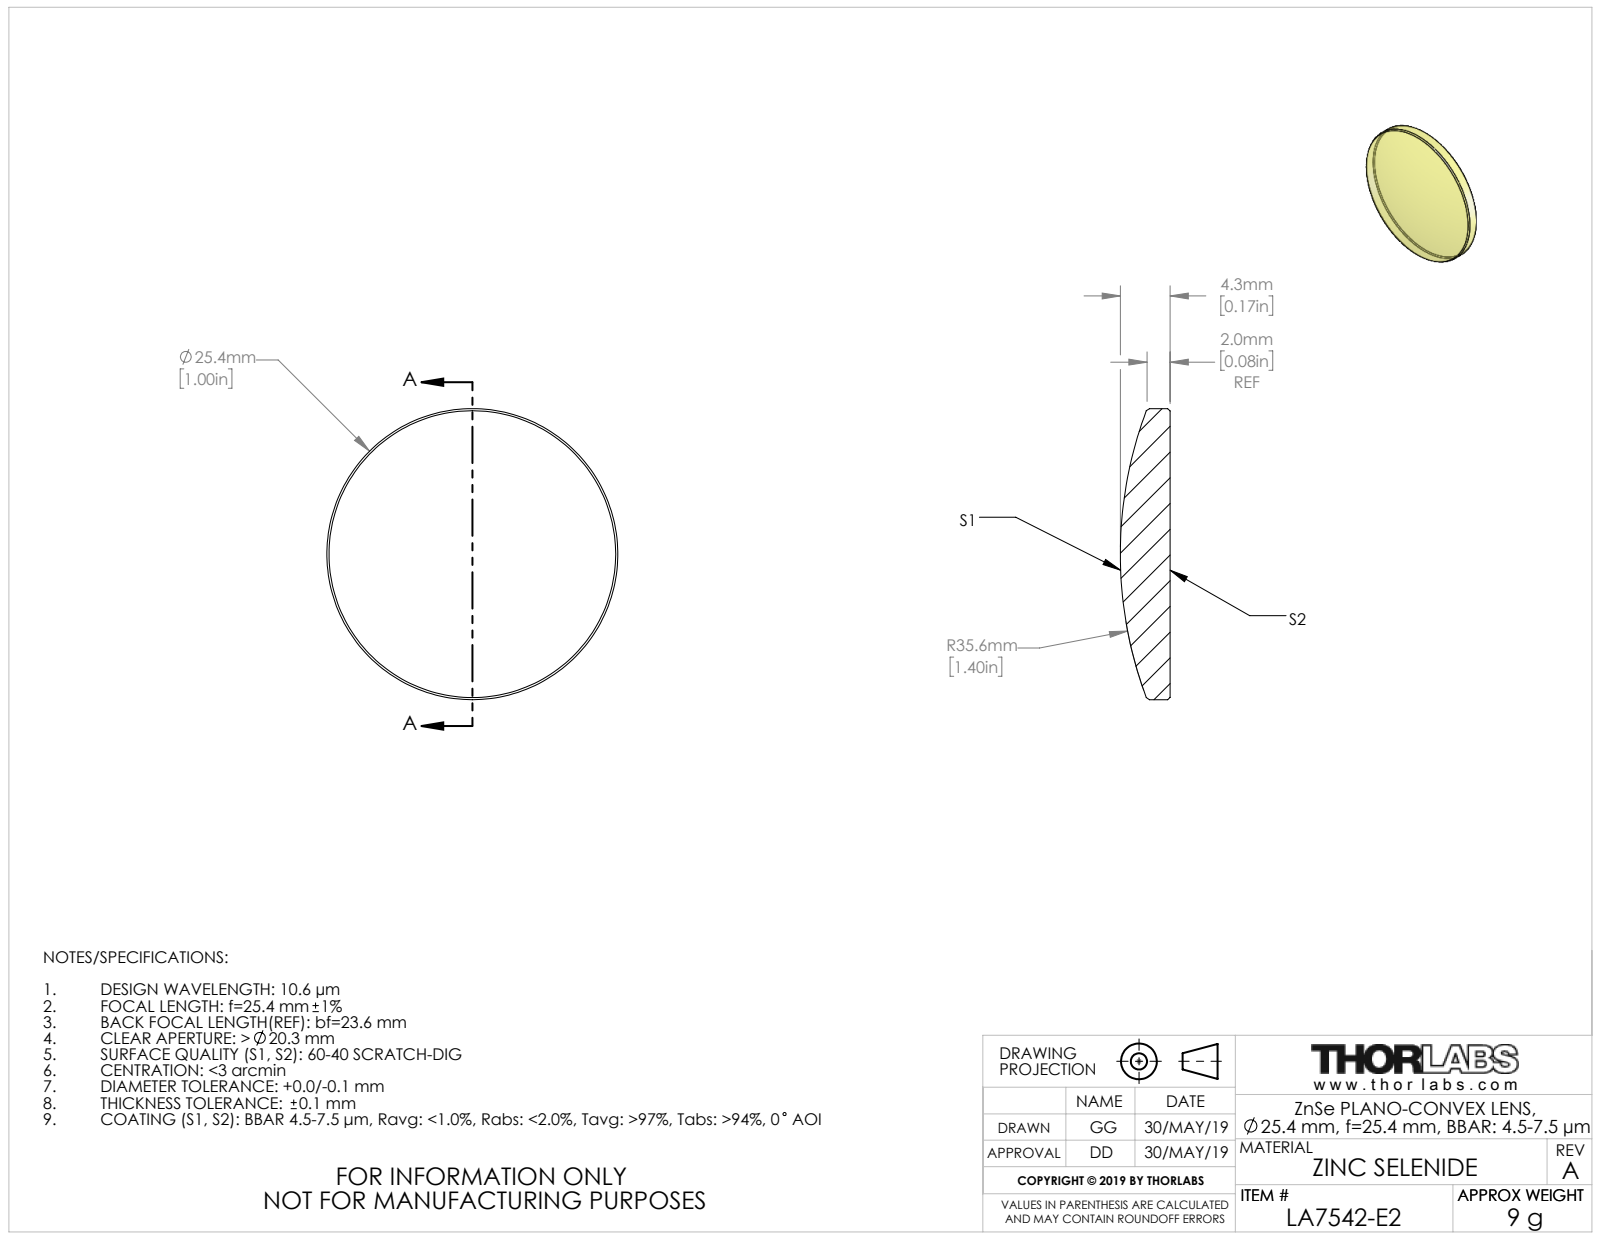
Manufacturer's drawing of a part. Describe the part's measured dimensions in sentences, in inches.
The part is named "TTN047584-E0W". Its 3-D file was written by "SolidWorks 2018 (CONFIG_CONTROL_DESIGN)". It is 1 solid with 9 faces: 1 planar, 2 cylindrical and 6 other. Overall it measures 1 by 1 by 0.171 inches. Its volume is 0.098 cubic inches and its surface area 1.823 square inches. Round bosses or shafts: 1 of diameter 1.
